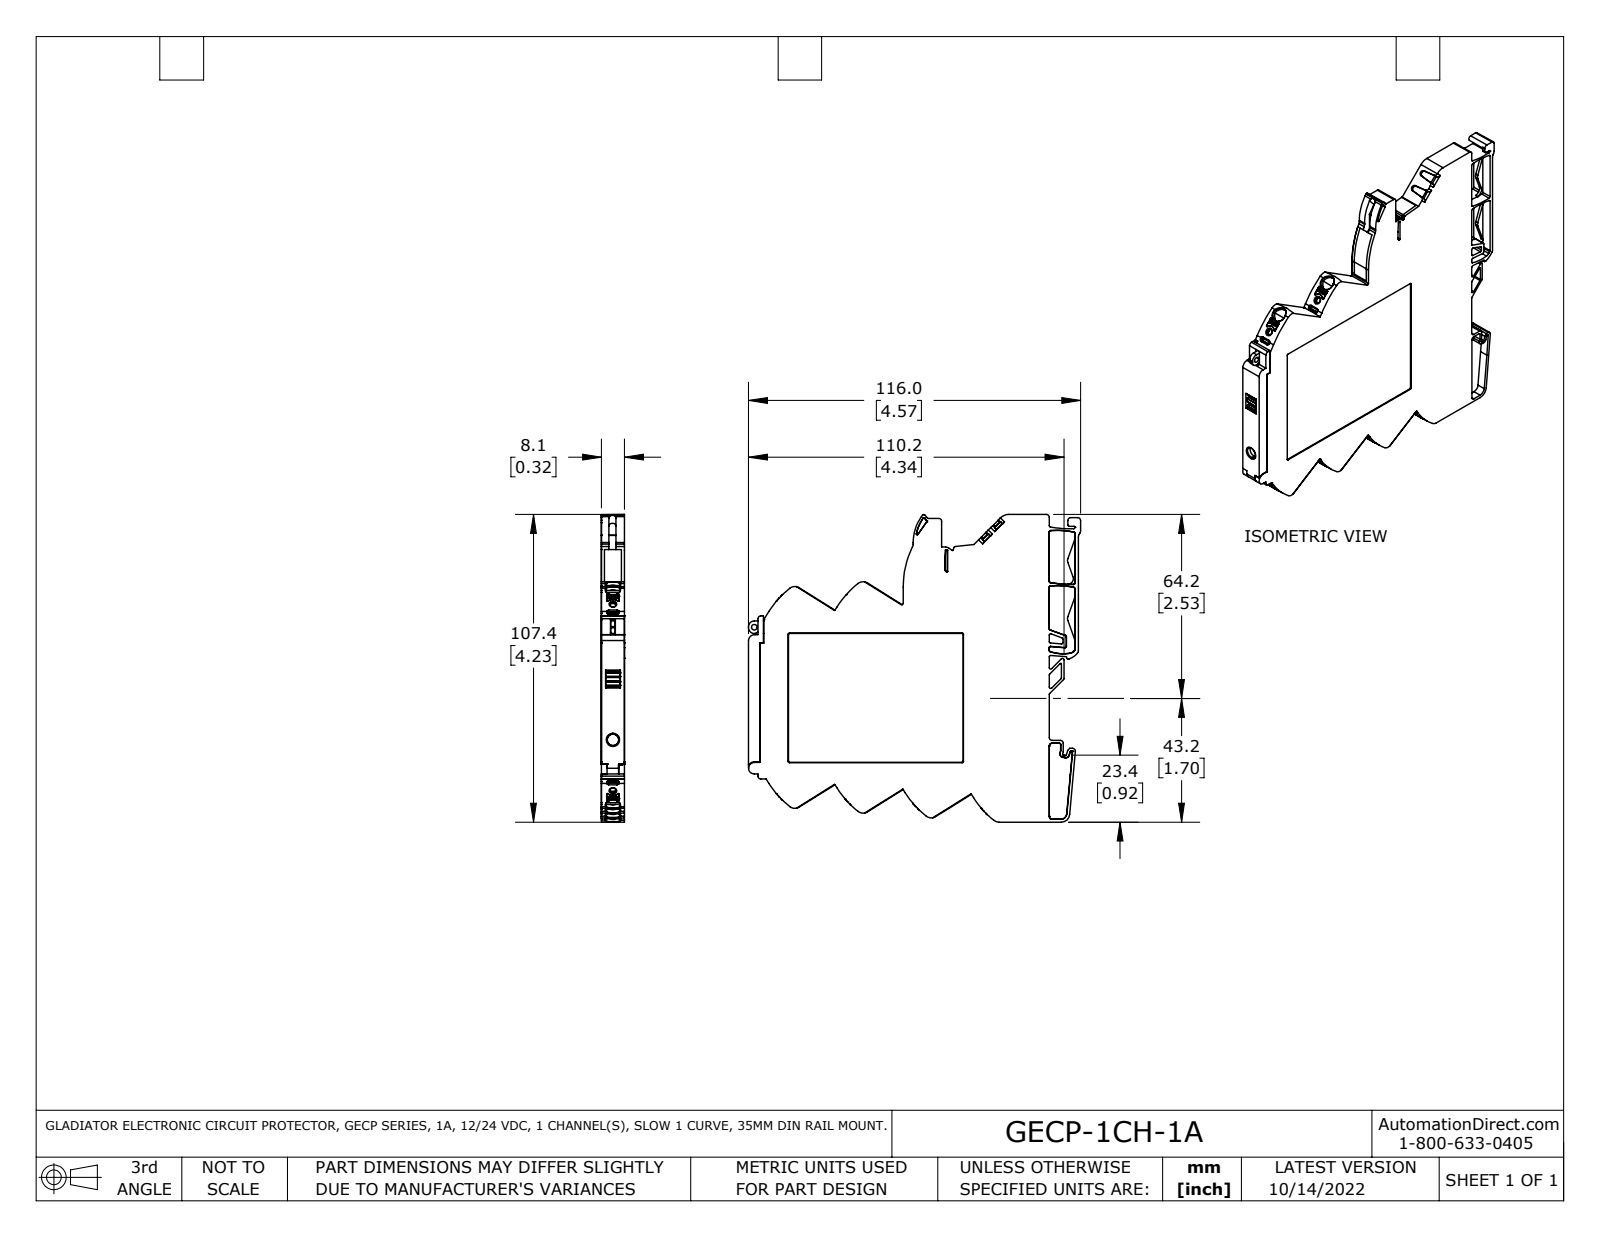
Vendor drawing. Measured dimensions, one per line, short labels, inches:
name: GECP-1CH-1A
written by: SolidWorks 2021 (AUTOMOTIVE_DESIGN)
unit: in
bodies: 1 solid, 1182 faces (549 planar, 466 cylindrical, 167 other)
size: 4.567 × 4.241 × 0.319
volume: 4.341 in³; area: 46.72 in²
holes: 6× ⌀0.083, 1× ⌀0.078, 1× ⌀0.087
bosses: 1× ⌀0.083
rounds: 58× R0.02, 45× R0.039, 43× R0.008, 28× R0.01, 27× R0.012, 13× R0.079, 12× R0.009, 12× R1.299
face distances: 0.319, 0.311, 0.309, 0.317, 0.201, 0.157, 0.118, 0.354, 3.935, 4.093
hole spacings: 0.559, 1.118, 0.559, 1.677, 1.937
